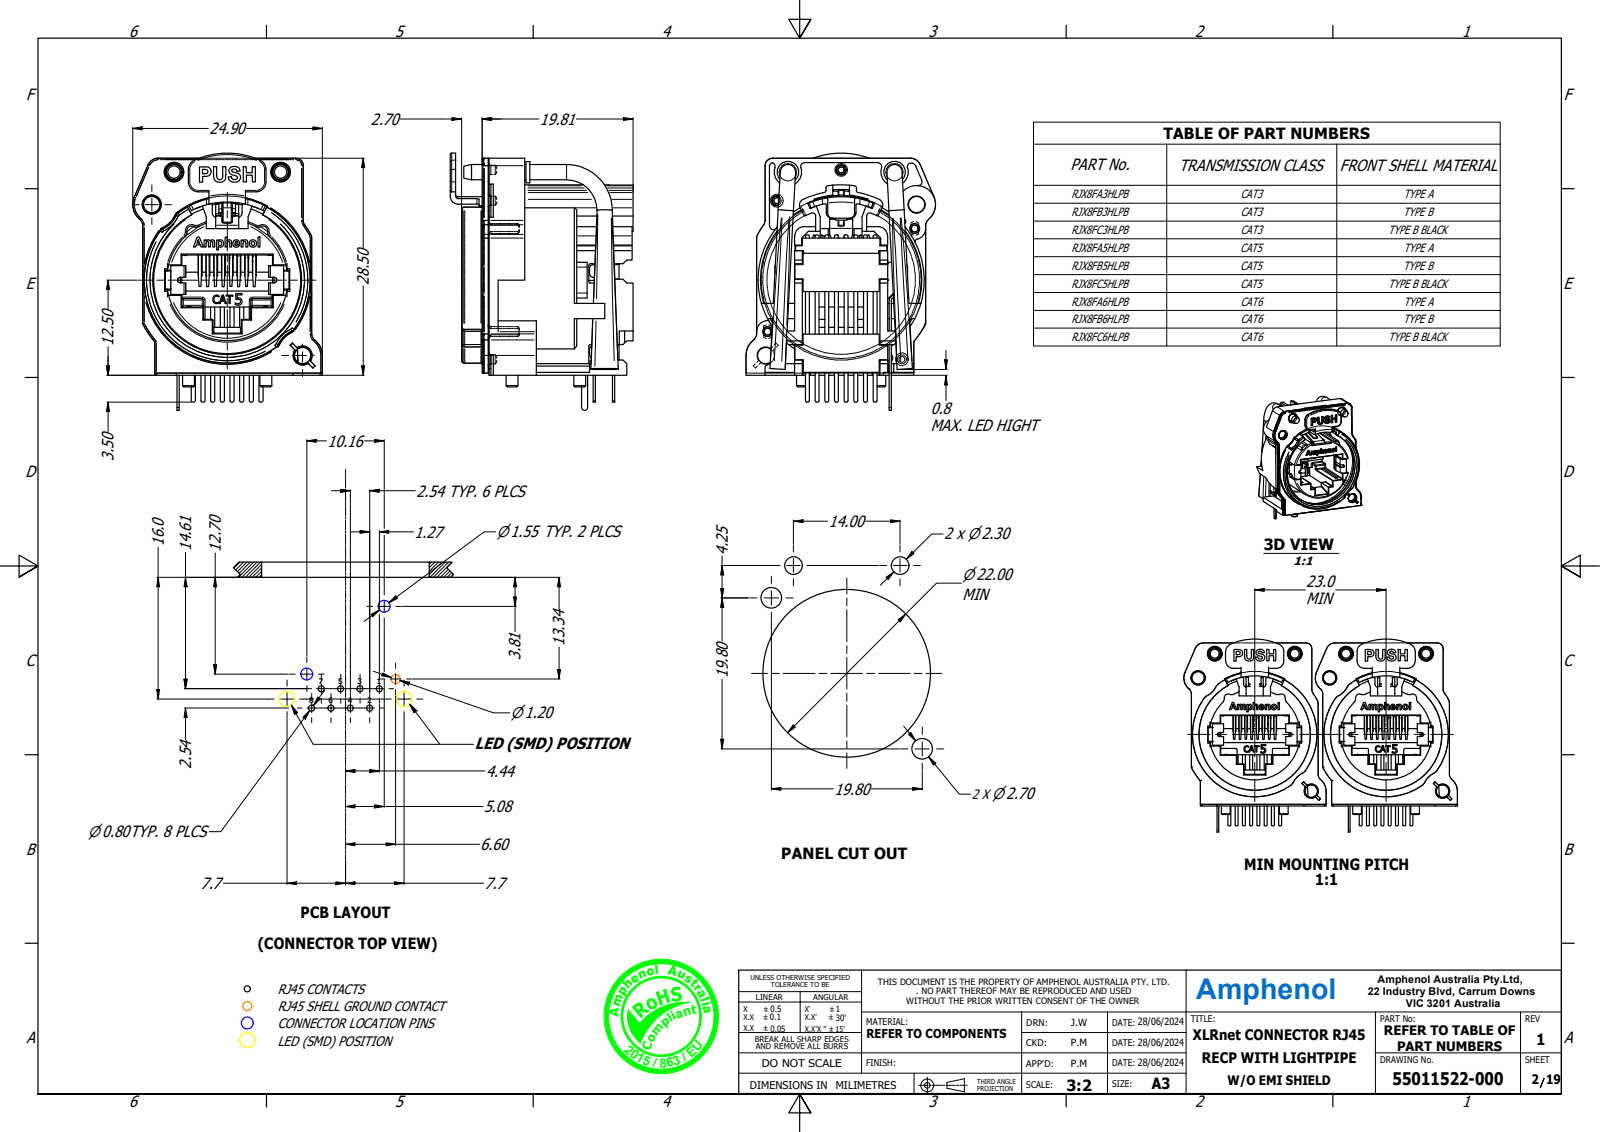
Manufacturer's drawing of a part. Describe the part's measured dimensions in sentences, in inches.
The part is named "55011522-000_Simplify_1". Its 3-D file was written by "Autodesk Inventor 2022 (AUTOMOTIVE_DESIGN)". It is 1 solid with 1105 faces: 668 planar, 230 cylindrical and 207 other. Overall it measures 1.33 by 0.98 by 0.945 inches. Its volume is 0.485 cubic inches and its surface area 10.6 square inches. Round holes: 3 of diameter 0.053, 2 of diameter 0.085, 2 of diameter 0.091, 2 of diameter 0.094, 2 of diameter 0.102, 1 of diameter 0.051, 1 of diameter 0.768, 1 of diameter 0.774, 1 of diameter 0.811. Round bosses or shafts: 4 of diameter 0.047, 2 of diameter 0.11, 2 of diameter 0.098, 2 of diameter 0.079, 2 of diameter 0.061, 2 of diameter 0.051, 1 of diameter 0.858. Partial cylindrical surfaces (rounded edges, fillets, slot ends): 21 of radius 0.012, 13 of radius 0.008, 11 of radius 0.005, 11 of radius 0.02, 10 of radius 0.031, 7 of radius 0.039, 6 of radius 0.016, 4 of radius 0.01. The main face-to-face distances are 0.031, 0.083, 0.677, 0.079, 0.672, 0.036, 0.708, 0.138, 0.115, 0.594. The hole center spacings are 0.551, 0.622, 0.157, 0.203, 0.276, 0.276, 0.369, 0.429.
